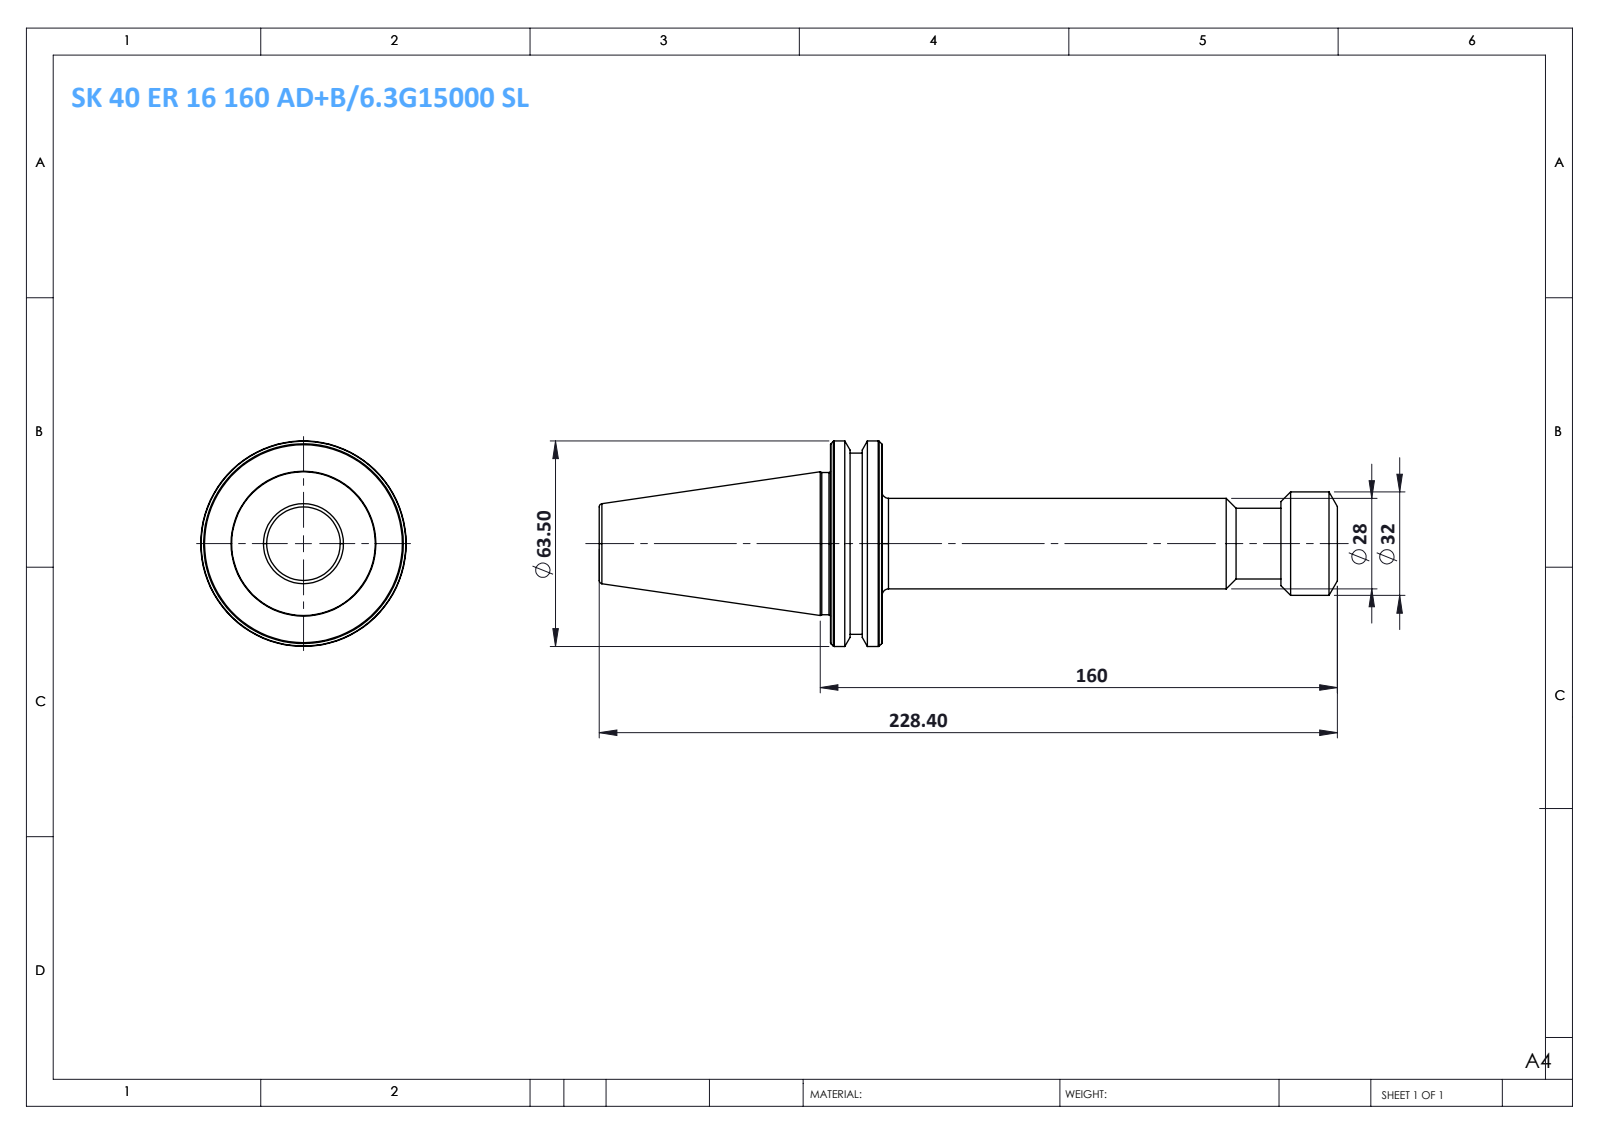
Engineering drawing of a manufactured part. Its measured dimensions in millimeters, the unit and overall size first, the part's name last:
Units: millimetres
Overall size (bounding box): 228.4 × 63.54 × 63.54
Round bosses / shafts (diameter × count): ⌀63.54 ×1, ⌀56.04 ×1, ⌀44 ×1, ⌀32 ×1, ⌀28 ×1, ⌀21.9 ×1
Main face-to-face distances: 15.92, 140.89, 156.81, 228.4, 87.51, 71.59, 150.79, 9.9, 6.02, 77.61
Volume: 202 691 mm³ · Surface area: 29 509 mm²
Bodies: 1 solid, 53 faces (7 planar, 14 cylindrical, 32 other)
Part name (STEP PRODUCT): SK 40 ER 16 160 AD-6.3G15000 SL
STEP written by: SolidWorks 2014 (CONFIG_CONTROL_DESIGN)
